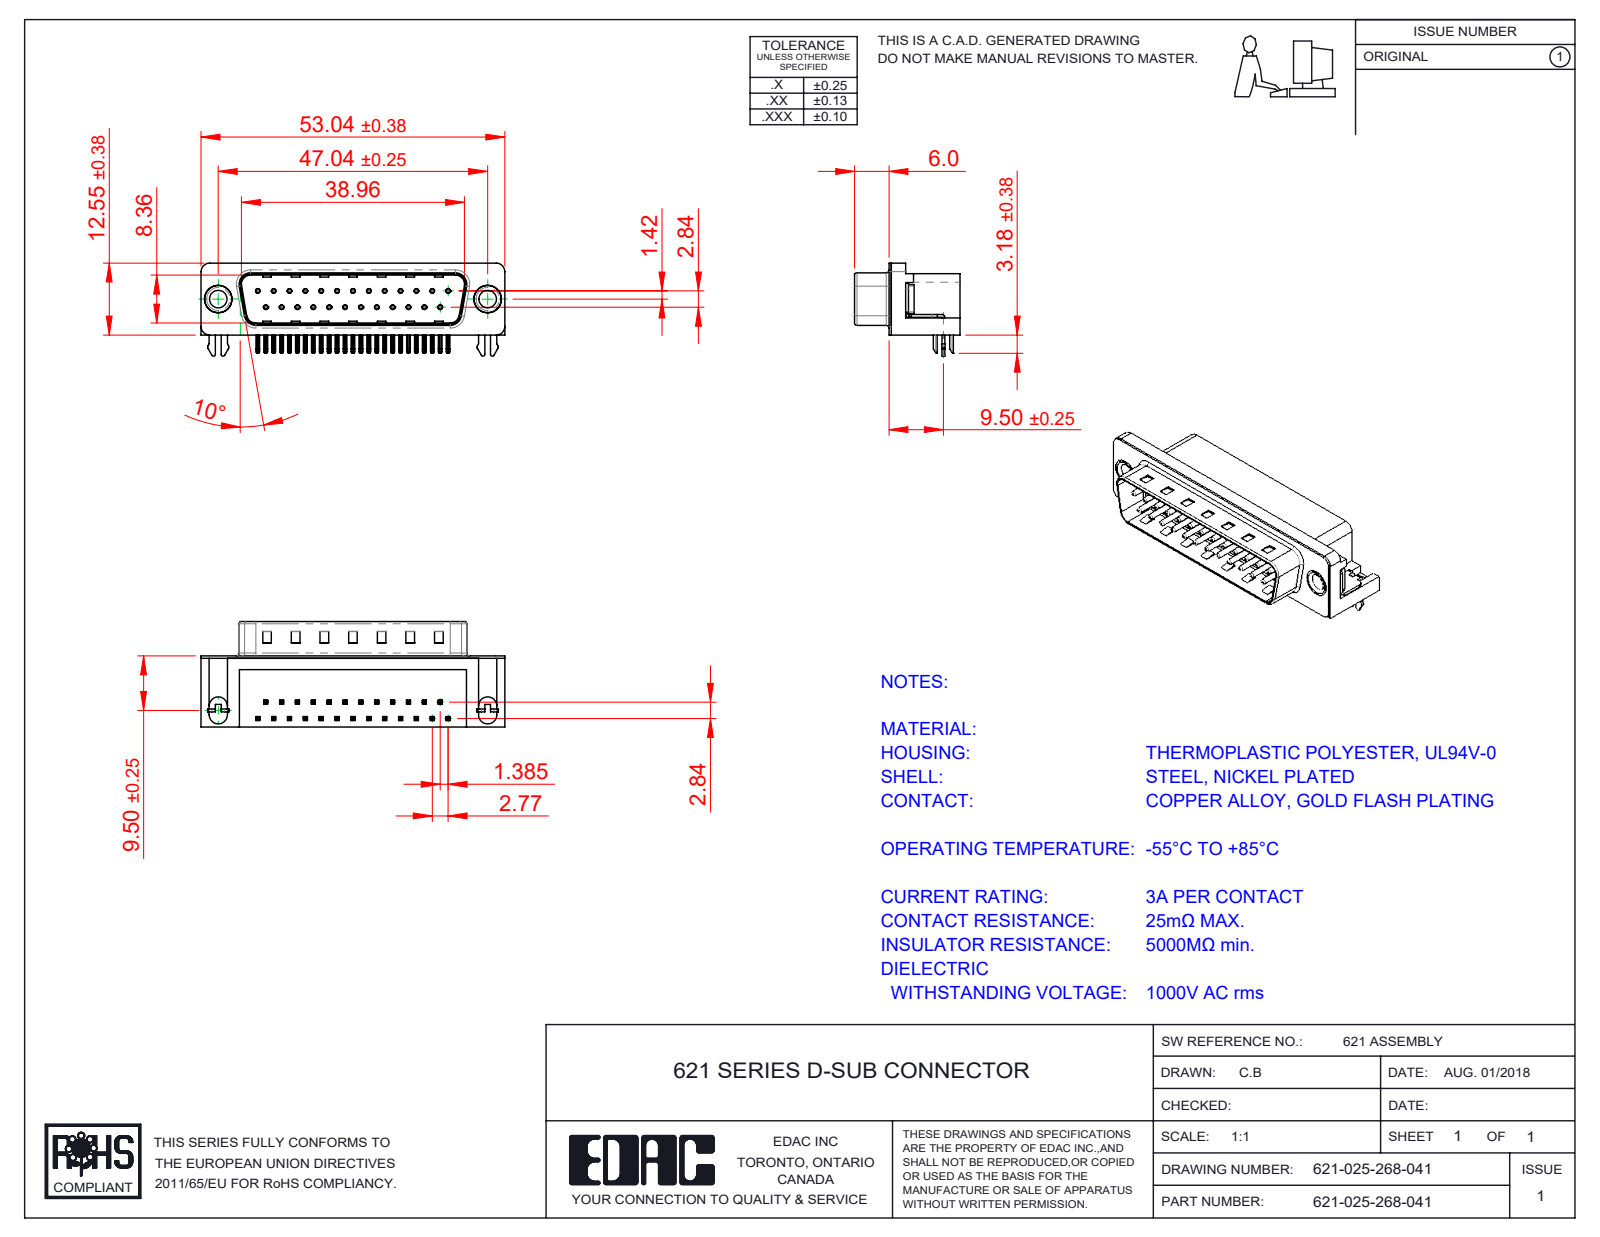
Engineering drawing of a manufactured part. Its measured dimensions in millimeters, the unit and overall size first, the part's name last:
Units: millimetres
Overall size (bounding box): 53.04 × 18.4 × 16.25
Round holes (diameter × count): ⌀0.35 ×25, ⌀0.8 ×25, ⌀2 ×2, ⌀3.05 ×2, ⌀4 ×2, ⌀4.8 ×2, ⌀5 ×2
Round bosses / shafts (diameter × count): ⌀0.75 ×25, ⌀4.9 ×2, ⌀4.75 ×2, ⌀3.85 ×2, ⌀3 ×2
Partial cylindrical surfaces — rounded edges, fillets, slot ends (radius × count): R0.25 ×112, R0.12 ×50, R1 ×16, R0.5 ×9, R1.6 ×8, R1.5 ×7, R0.9 ×4, R2 ×4
Main face-to-face distances: 0.4, 12, 10.35, 2.1, 8.76, 10.46, 1.7, 10.86, 12.4, 9
Hole centre spacings: 3.16, 2.77, 5.54, 8.31, 11.08, 13.85, 16.62, 5.03
Volume: 6 345 mm³ · Surface area: 7 734 mm²
Bodies: 31 solids, 2343 faces (1447 planar, 647 cylindrical, 249 other)
Part name (STEP PRODUCT): 621 Contact Top; 621 Contact Bottom; 621 Shell_25 Socket; 621 Thru Hole Rivet (+3 more)
STEP written by: SolidWorks 2016 (CONFIG_CONTROL_DESIGN)
